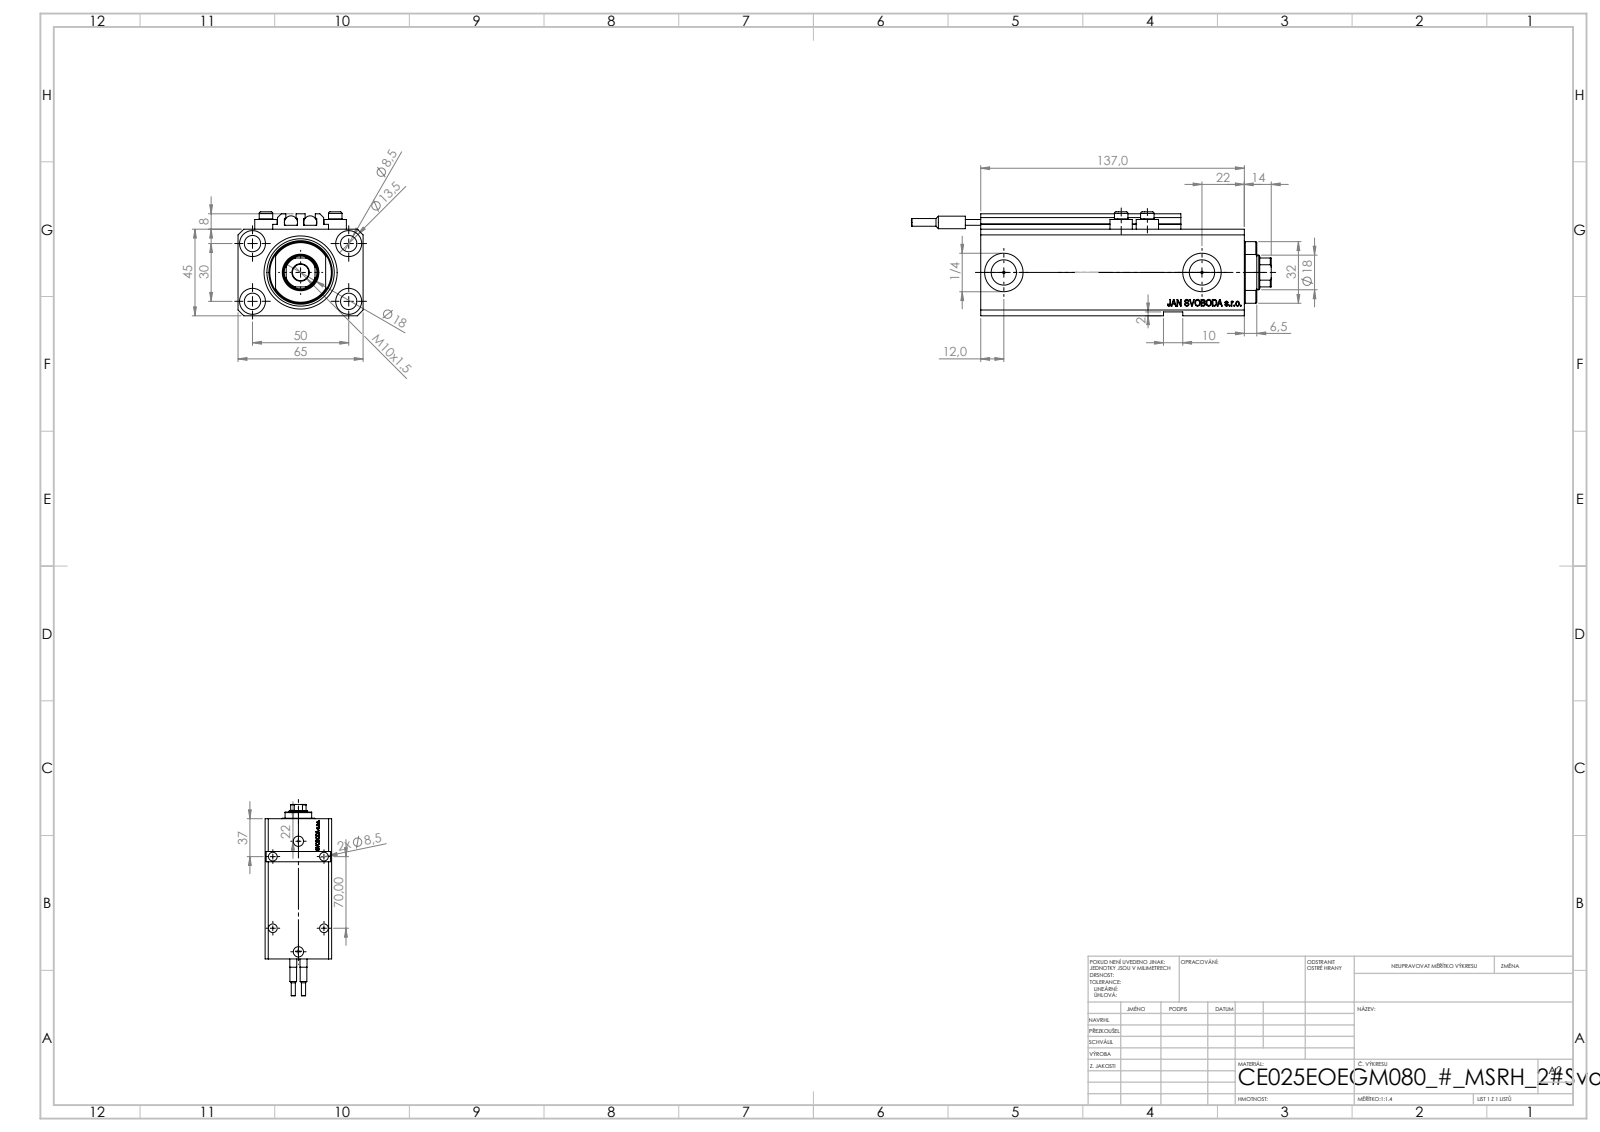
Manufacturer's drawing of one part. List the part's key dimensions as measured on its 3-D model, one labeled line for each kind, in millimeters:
Part name (STEP PRODUCT): V250CE_VC_E; ALLEN BOLT V250CE; SWITCH_V250CE; V250CE_E_Body (+1 more)
STEP written by: SolidWorks 2019 (CONFIG_CONTROL_DESIGN)
Units: millimetres
Bodies: 10 solids, 1139 faces (543 planar, 158 cylindrical, 438 other)
Overall size (bounding box): 187 × 65 × 54
Volume: 354 066 mm³ · Surface area: 96 296 mm²
Round holes (diameter × count): ⌀8.5 ×9, ⌀1.25 ×4, ⌀4 ×4, ⌀13.5 ×4, ⌀10 ×2, ⌀13.16 ×2, ⌀20 ×2, ⌀18 ×1, ⌀25 ×1, ⌀38 ×1
Round bosses / shafts (diameter × count): ⌀11.6 ×4, ⌀7 ×4, ⌀6.8 ×2, ⌀6.5 ×2, ⌀4 ×2
Partial cylindrical surfaces — rounded edges, fillets, slot ends (radius × count): R0.2 ×10, R8.5 ×1, R16 ×1
Main face-to-face distances: 45, 65, 47, 2, 2.5, 10, 3, 123, 14, 137
Hole centre spacings: 29.15, 50, 13.6, 15.12, 27.89, 30, 33.61, 33.62
